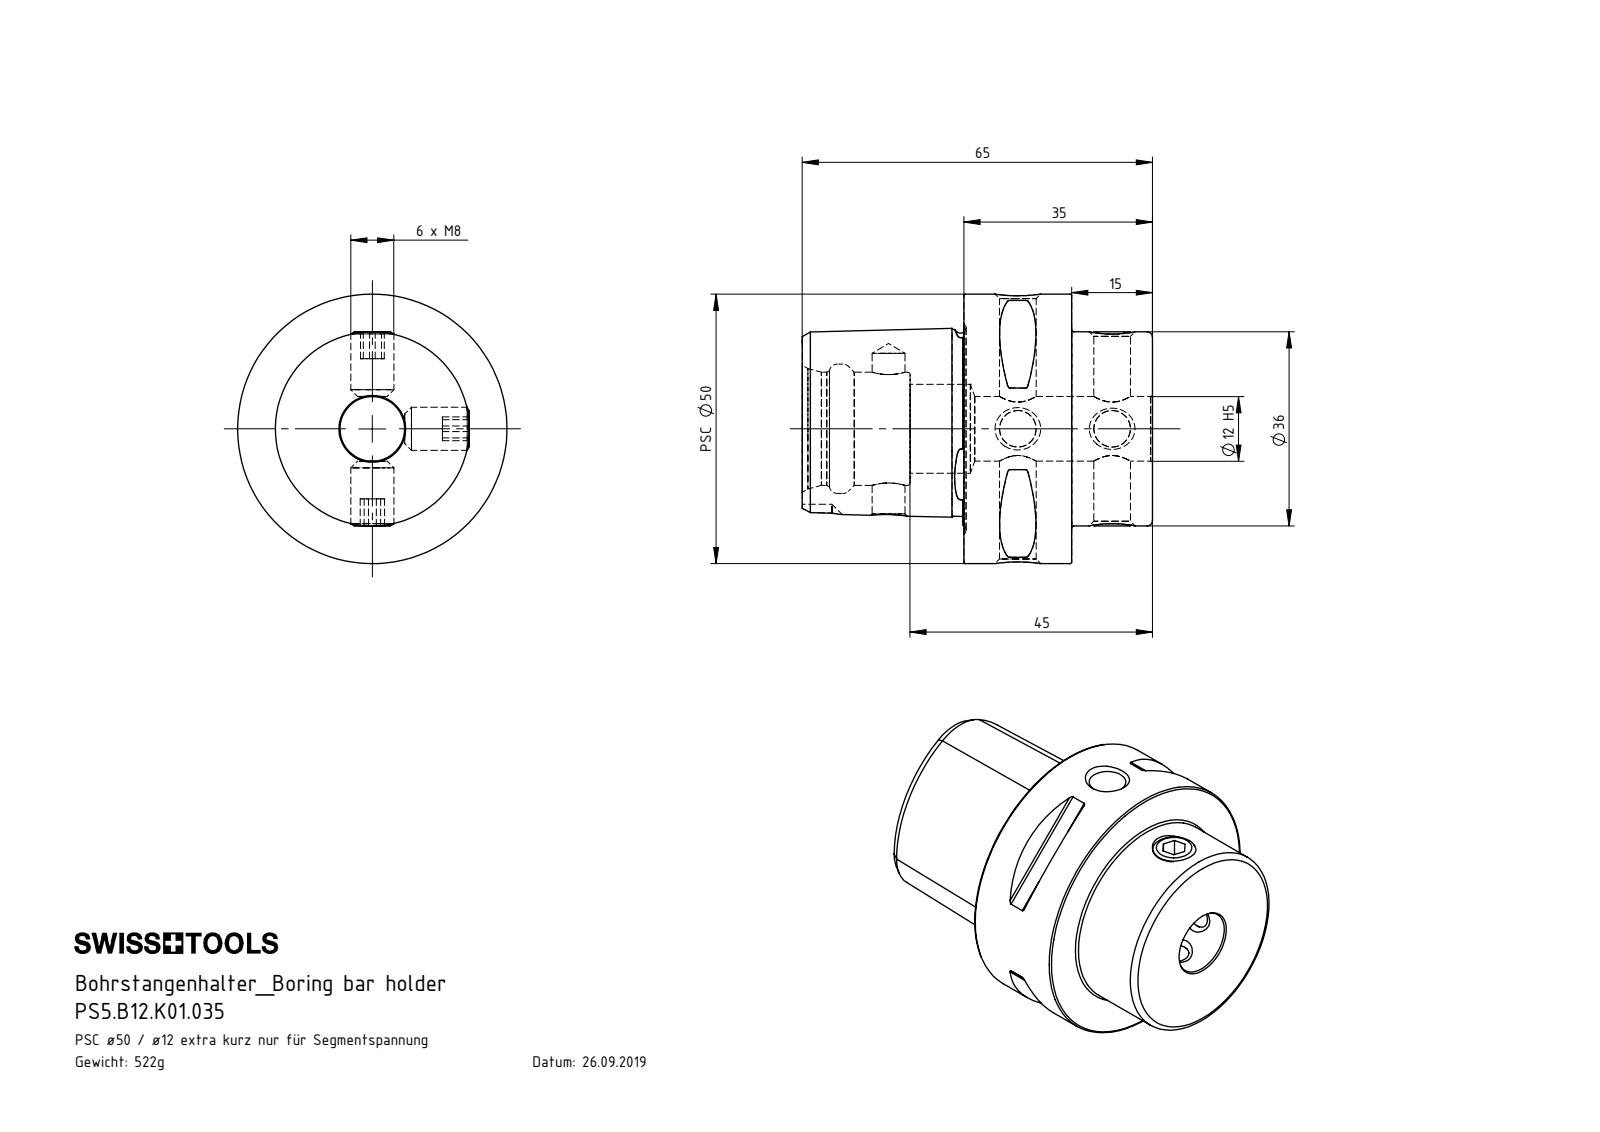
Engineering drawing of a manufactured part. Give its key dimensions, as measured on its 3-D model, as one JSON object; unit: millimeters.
{"part_name": "PS5.B12.K01.035; PS5-B12.K01.035_A; ISO 4026 - M8 x 12_PreviewCfg", "step_written_by": "SolidWorks 2017 (AUTOMOTIVE_DESIGN)", "units": "millimeters", "bodies": {"solids": 7, "faces": 171, "planar": 74, "cylindrical": 30, "other": 67}, "overall_size": [65, 50, 50], "volume_mm3": 66502, "surface_area_mm2": 19278, "round_holes": [[6.8, 4], [6.1, 1], [12, 1], [16.5, 1], [21, 1], [24, 1]], "round_bosses_or_shafts": [[8, 4], [50, 1], [36, 1]], "partial_cylinders_radius": [[0.5, 8], [4, 1]], "face_to_face_distances": [20, 15, 35, 30, 50, 65, 4, 19.18, 12, 44.4], "hole_center_spacings": [17.5, 24, 41.5]}
